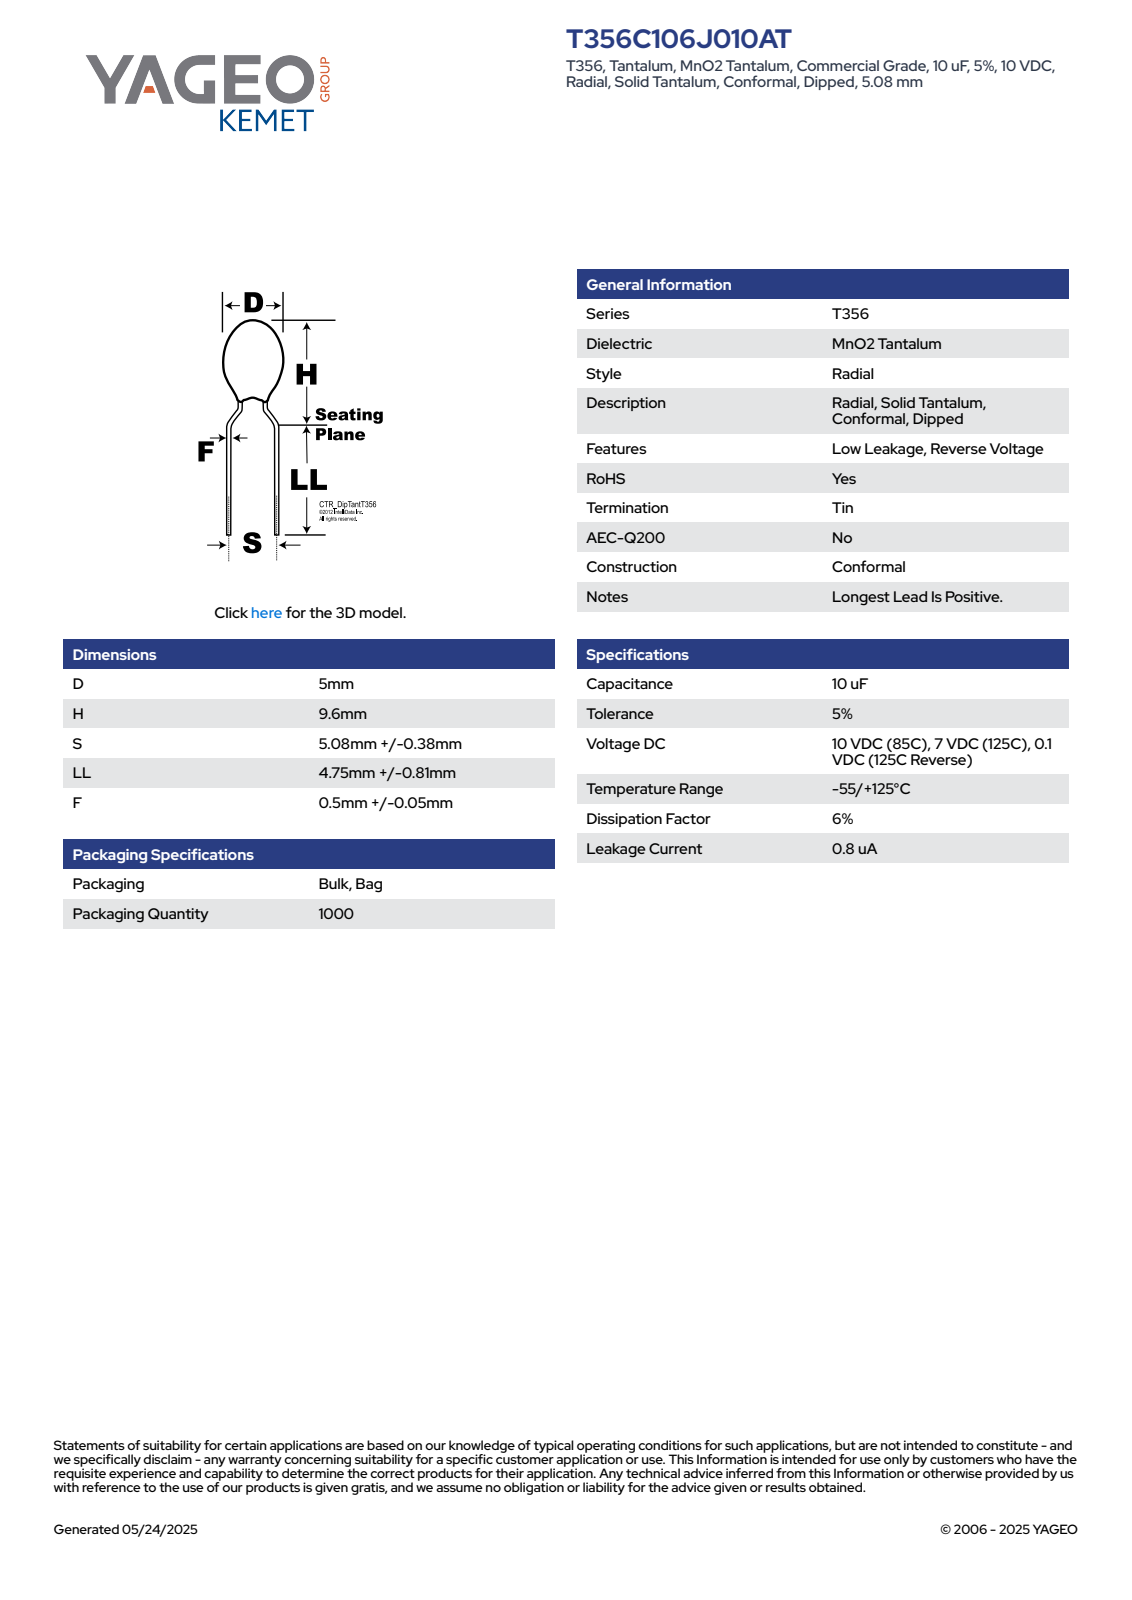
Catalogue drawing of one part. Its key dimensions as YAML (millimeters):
part_name: "CTR_T356_D5H9.6S5.08LL5.56F0.55"
step_written_by: "SolidWorks 2014 (AUTOMOTIVE_DESIGN)"
units: millimeters
bodies: {solids: 1, faces: 100, planar: 27, cylindrical: 18, other: 55}
overall_size: [15.16, 5.63, 5]
volume: 123
surface_area: 156
round_bosses_or_shafts:
  - {diameter: 0.55, count: 6}
  - {diameter: 5, count: 1}
partial_cylinders:
  - {radius: 2.49, count: 1}
face_to_face_distances: [6.7, 8.46, 15.16, 12.88, 4.42, 2.28, 11.97, 3.51, 0.91, 3.19]
